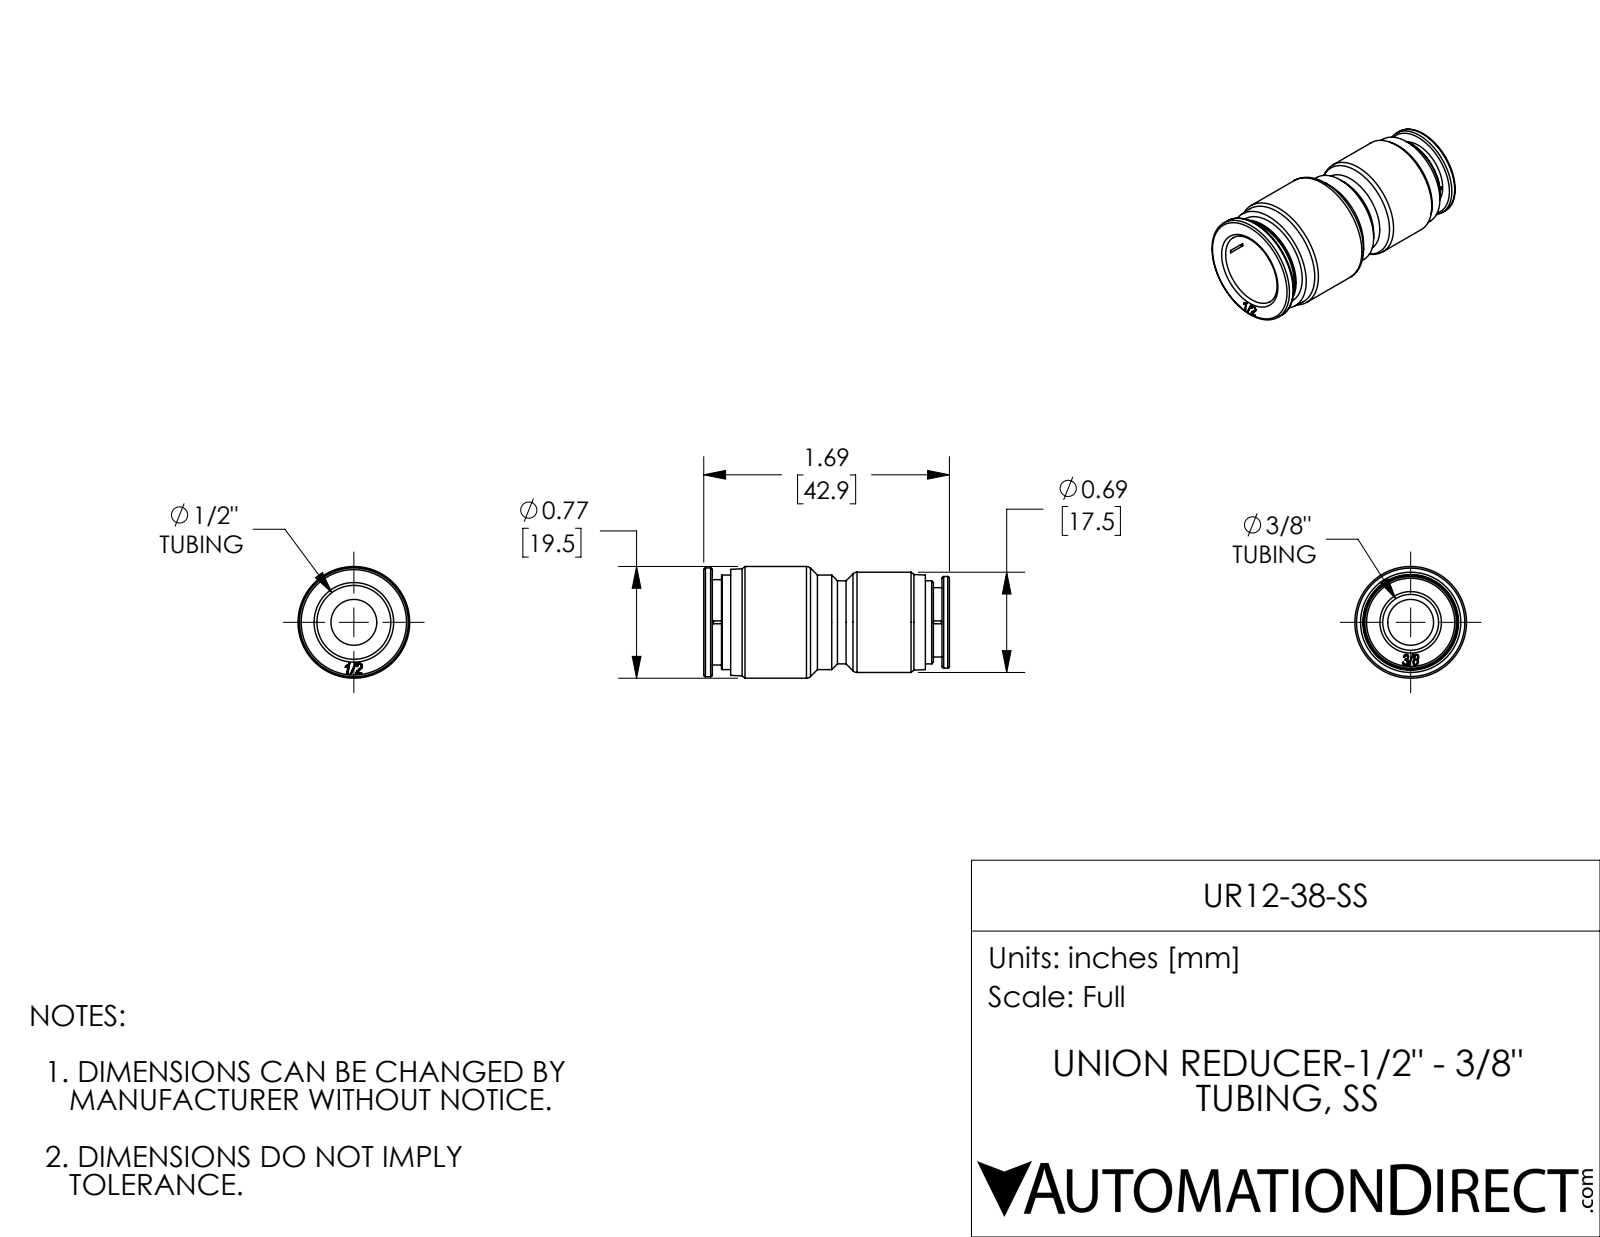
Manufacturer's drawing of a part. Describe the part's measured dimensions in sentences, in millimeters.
The part is named "UR12-38-SS". Its 3-D file was written by "SolidWorks 2017 (AUTOMOTIVE_DESIGN)". It is 1 solid with 168 faces: 52 planar, 28 cylindrical and 88 other. Overall it measures 42.9 by 19.5 by 19.5 millimeters. Its volume is 5 850 cubic millimeters and its surface area 4 947 square millimeters. Round holes: 1 of diameter 8, 1 of diameter 9.8, 1 of diameter 12.9, 1 of diameter 15.1. Round bosses or shafts: 1 of diameter 19.5, 1 of diameter 19, 1 of diameter 17.5, 1 of diameter 16.5, 1 of diameter 16, 1 of diameter 14.9, 1 of diameter 14.5, 1 of diameter 12.1. The main face-to-face distances are 1.5, 40.1, 42.9, 41.4, 19.8, 21.1, 20.3, 21.8, 1.3, 41.6.
